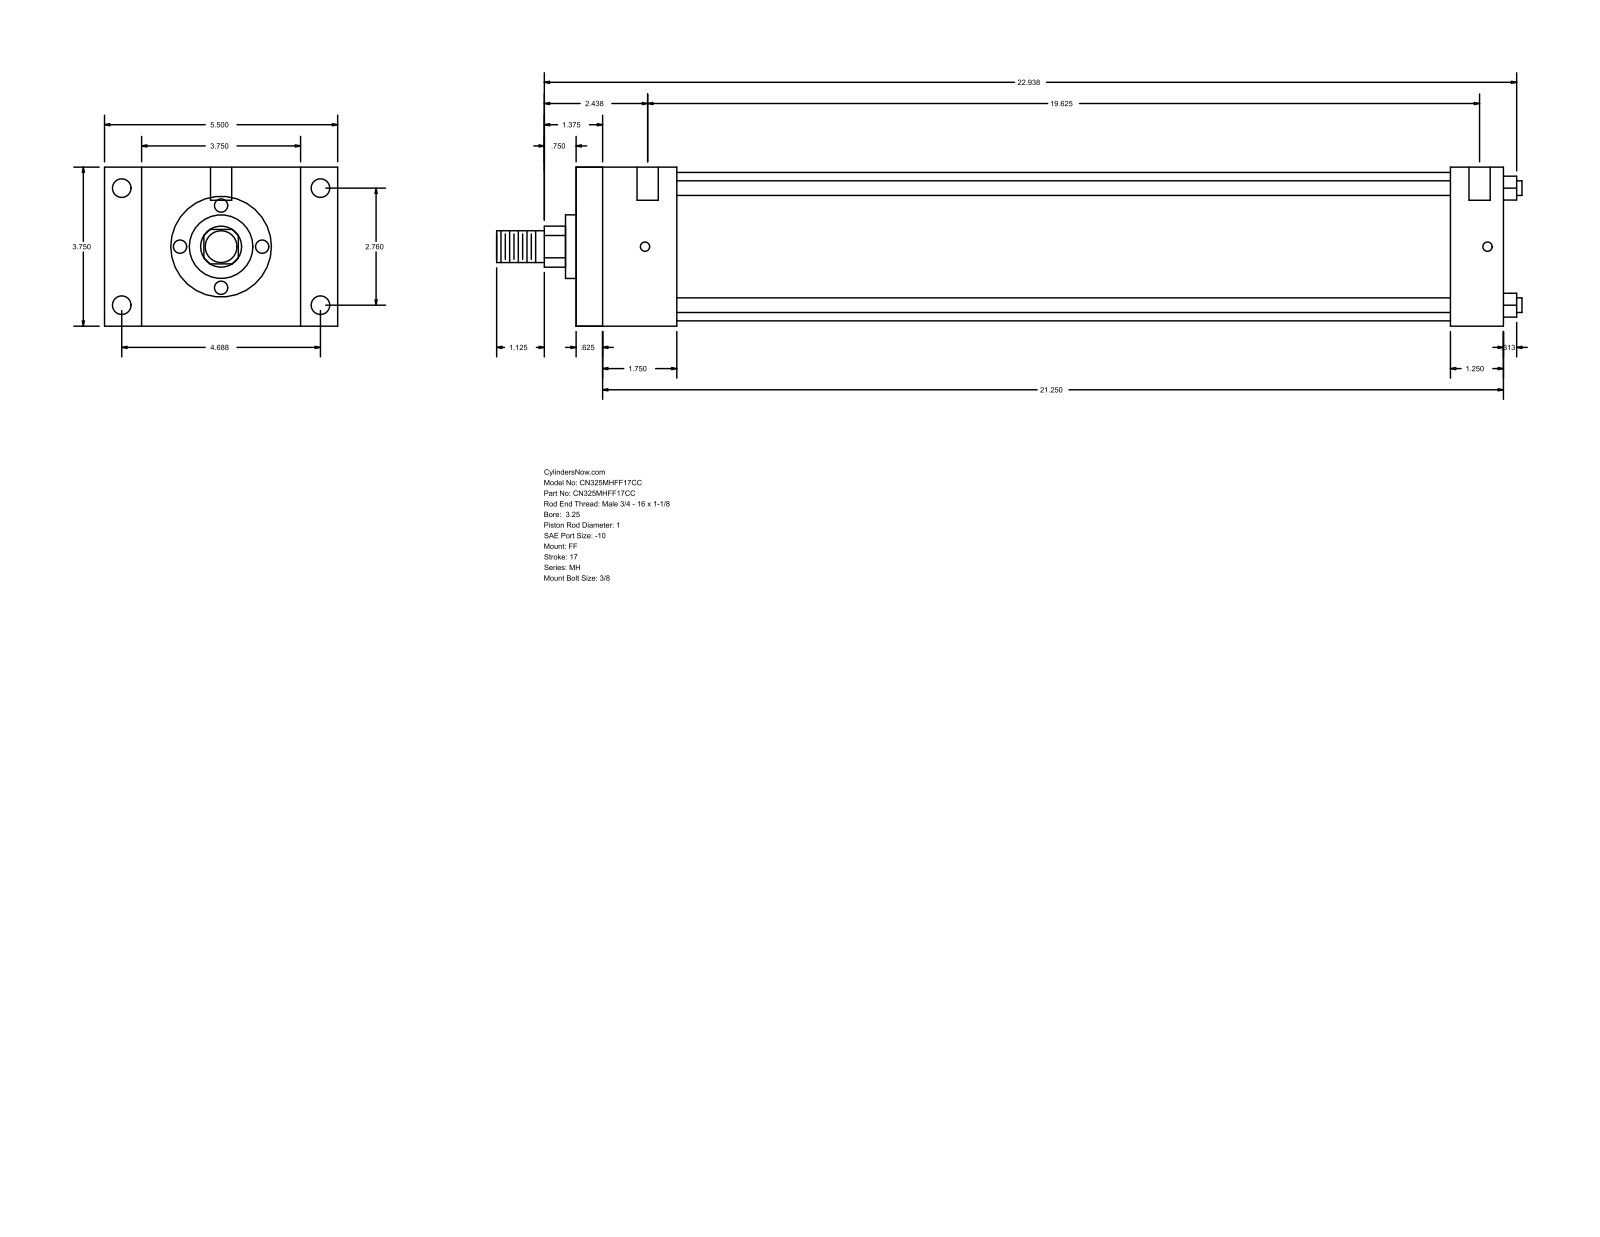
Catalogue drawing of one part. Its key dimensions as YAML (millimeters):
part_name: "MH_FF__0325_1"
step_written_by: "GSSL Pune (CONFIG_CONTROL_DESIGN)"
units: millimeters
bodies: {solids: 0, faces: 92, planar: 64, cylindrical: 28, other: 0}
overall_size: [614.36, 139.7, 95.25]
round_holes:
  - {diameter: 5.56, count: 4}
  - {diameter: 11.13, count: 4}
  - {diameter: 12.7, count: 2}
round_bosses_or_shafts:
  - {diameter: 8.76, count: 4}
  - {diameter: 88.9, count: 1}
  - {diameter: 38.1, count: 1}
  - {diameter: 25.4, count: 1}
  - {diameter: 19.05, count: 1}
partial_cylinders:
  - {radius: 12.29, count: 1}
face_to_face_distances: [95.24, 555.62, 15.87, 539.75, 22.23, 117.47, 523.87, 508, 31.75, 60.33]
hole_center_spacings: [70.1, 119.06, 138.16, 504.82, 1.58, 4.76, 498.48, 500.06]
